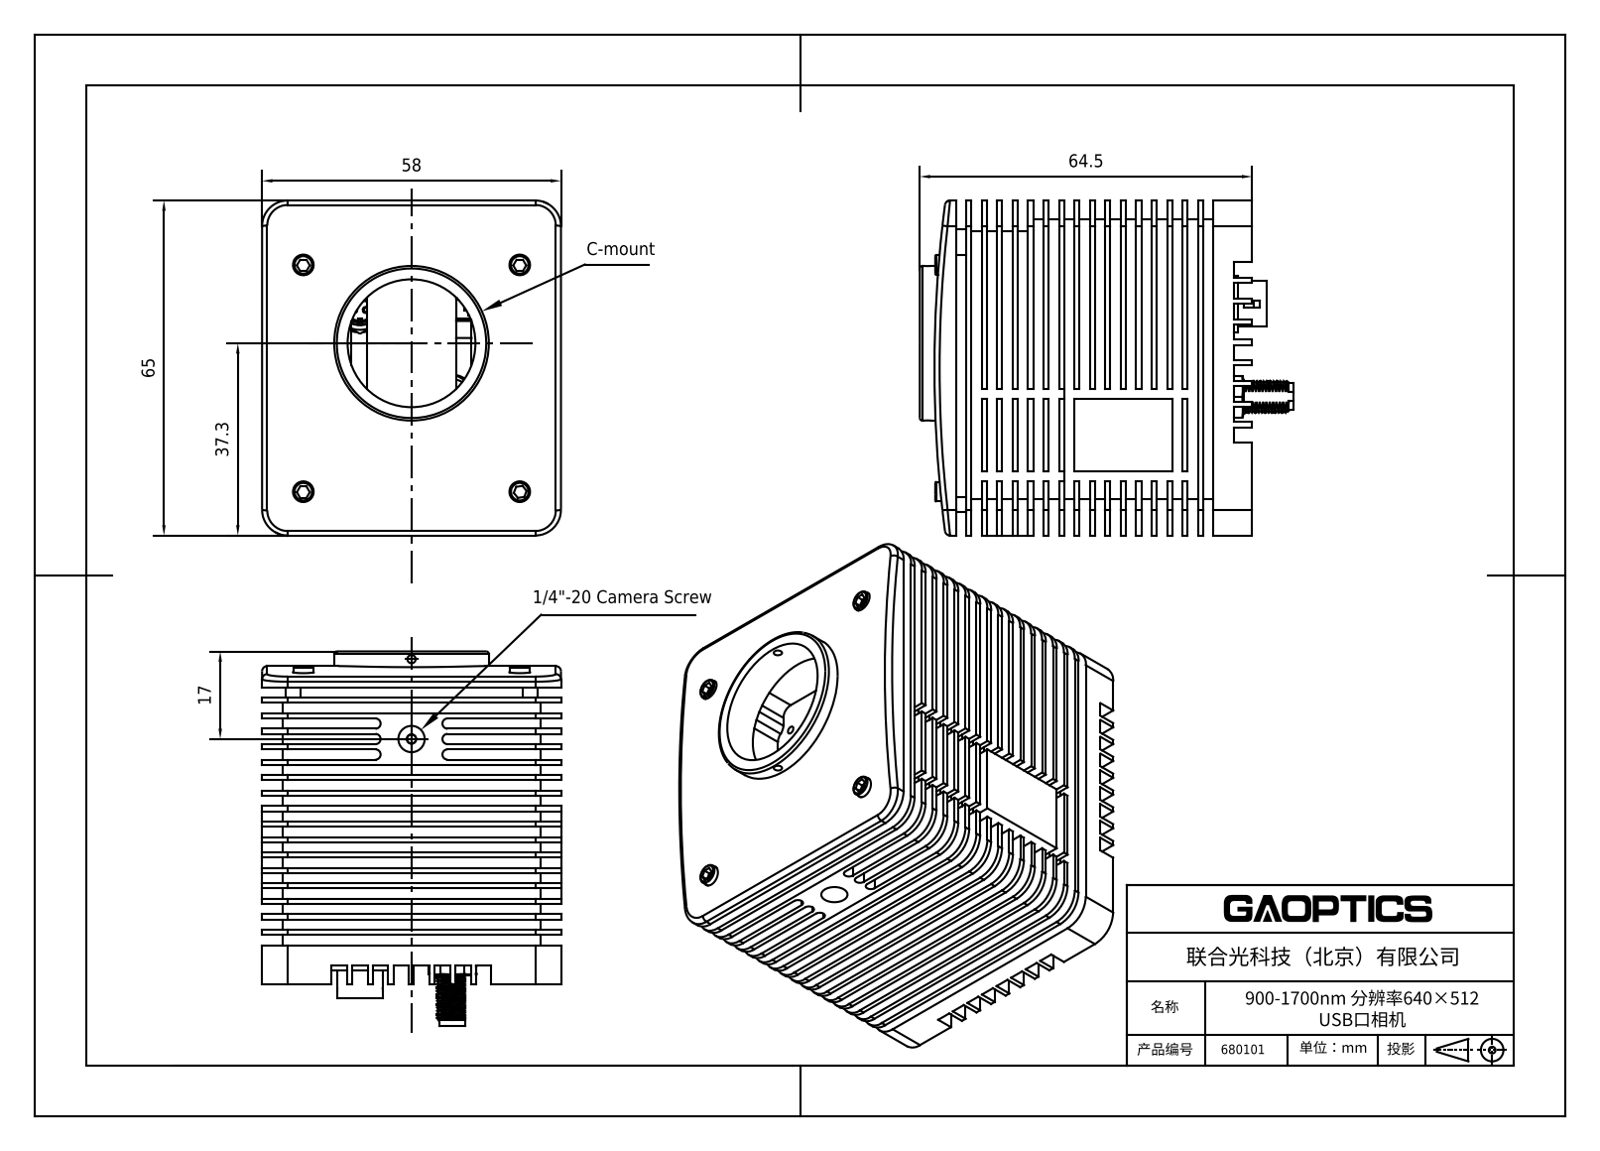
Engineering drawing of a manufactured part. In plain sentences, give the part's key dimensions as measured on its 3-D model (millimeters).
The part is named "HR10A-7R-4S; Mini USB机芯; miniusb; 前盖 (+8 more)". Its 3-D file was written by "SolidWorks 2014 (AUTOMOTIVE_DESIGN)". It is 17 solids with 1652 faces: 972 planar, 530 cylindrical and 150 other. Overall it measures 72.6 by 65 by 58 millimeters. Its volume is 77 183 cubic millimeters and its surface area 82 321 square millimeters. Round holes: 25 of diameter 1.6, 12 of diameter 2.2, 8 of diameter 4, 6 of diameter 0.8, 1 of diameter 0.5, 1 of diameter 0.6, 1 of diameter 1.5, 1 of diameter 1.8, 1 of diameter 2, 1 of diameter 2.9, 1 of diameter 4.6, 1 of diameter 5.11. Round bosses or shafts: 8 of diameter 3.8, 8 of diameter 2, 6 of diameter 1.2, 4 of diameter 0.46, 1 of diameter 30, 1 of diameter 11, 1 of diameter 9.4, 1 of diameter 8.9. Partial cylindrical surfaces (rounded edges, fillets, slot ends): 30 of radius 2, 24 of radius 3, 12 of radius 0.3, 12 of radius 4.1, 10 of radius 0.6, 10 of radius 1, 6 of radius 5, 4 of radius 1.5. The main face-to-face distances are 3, 2, 4, 6, 9, 45, 5, 1.5, 1, 42. The hole center spacings are 35.84, 37.3, 1.6, 2.26, 3.81, 4.64, 9.53, 18.61.
